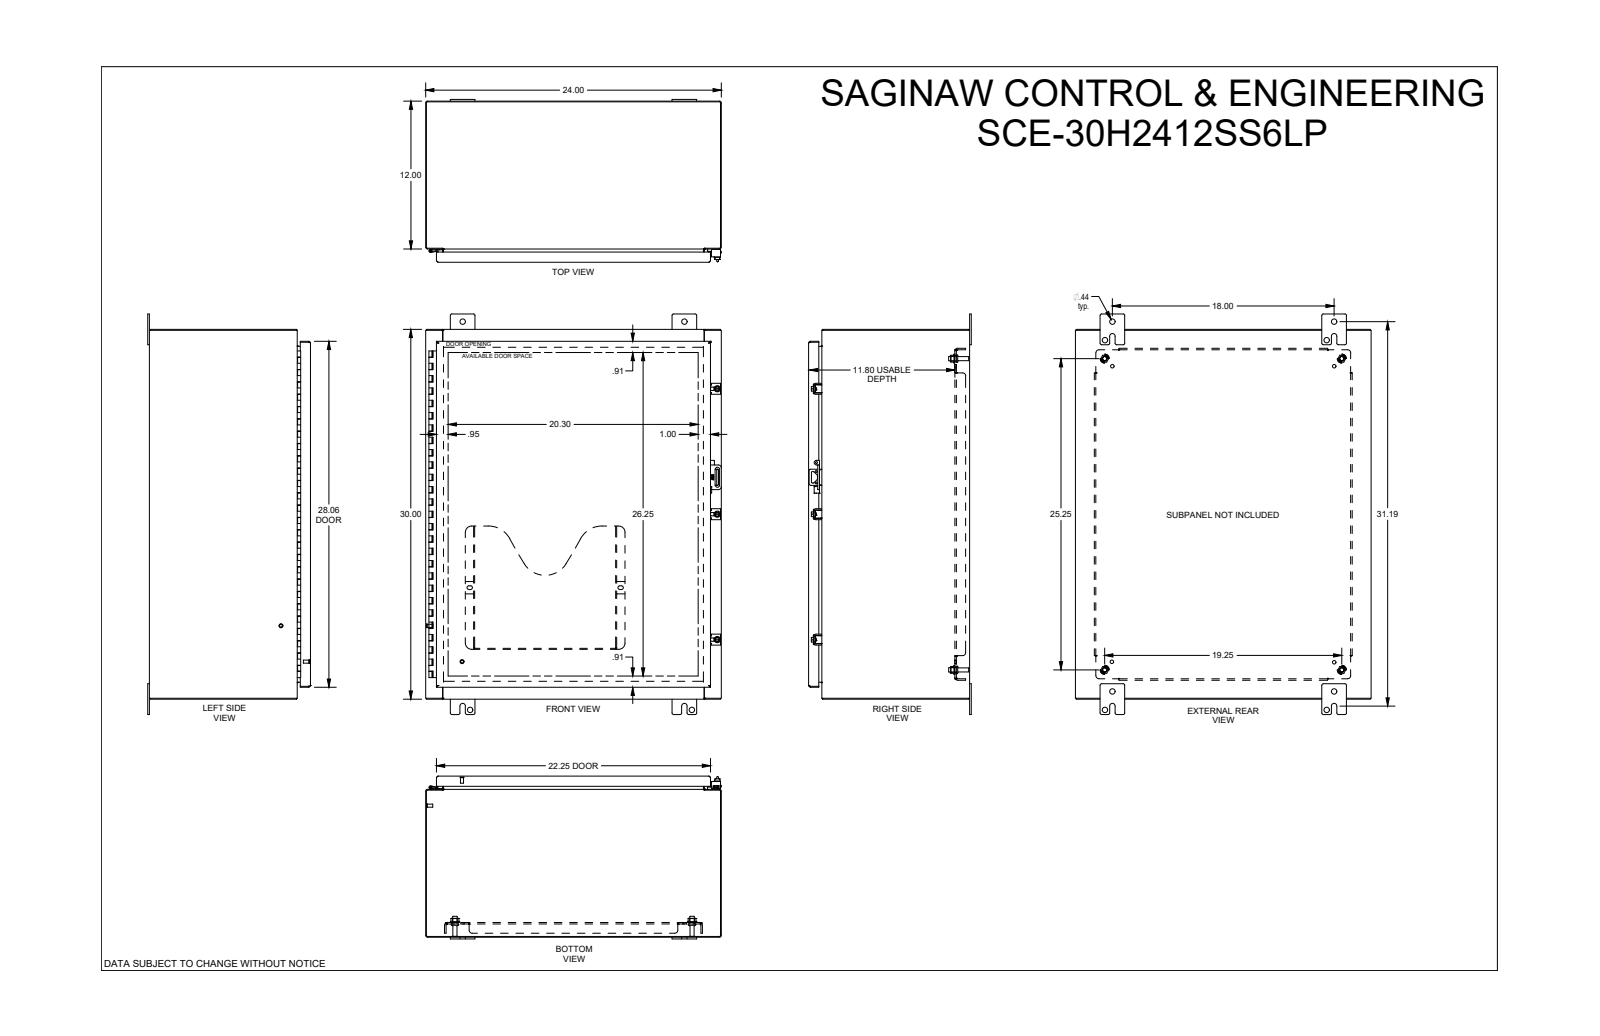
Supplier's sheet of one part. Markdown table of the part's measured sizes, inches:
| quantity | value |
| --- | --- |
| part name | SCE-30H2412SS6LP |
| STEP written by | SolidWorks 2019 (CONFIG_CONTROL_DESIGN) |
| units | inches |
| bodies | 0 solids, 3825 faces (1563 planar, 800 cylindrical, 1462 other) |
| overall size | 32.5 × 24 × 13.208 |
| round holes (diameter × count) | 0.437 × 8, 0.25 × 6, 0.19 × 5, 0.193 × 5, 0.203 × 5, 0.281 × 4, 0.367 × 4, 0.5 × 4, 0.16 × 2, 0.13 × 1, 0.132 × 1 |
| round bosses / shafts (diameter × count) | 0.248 × 8, 0.563 × 6, 0.256 × 5, 0.188 × 5, 0.366 × 4, 0.332 × 4, 0.25 × 4, 0.507 × 3 |
| partial cylindrical surfaces (radius × count) | 0.01 × 148, 0.015 × 44, 0.029 × 36, 0.06 × 29, 0.03 × 27, 0.125 × 27, 0.04 × 22, 0.07 × 14 |
| main face-to-face distances | 0.075, 23.925, 0.075, 12.998, 12.923, 1.2, 11.873, 13.073, 12.998, 29.925 |
| hole center spacings | 18, 0.515, 0.875, 6.375, 6.375, 12.75, 21.607, 30.884 |
